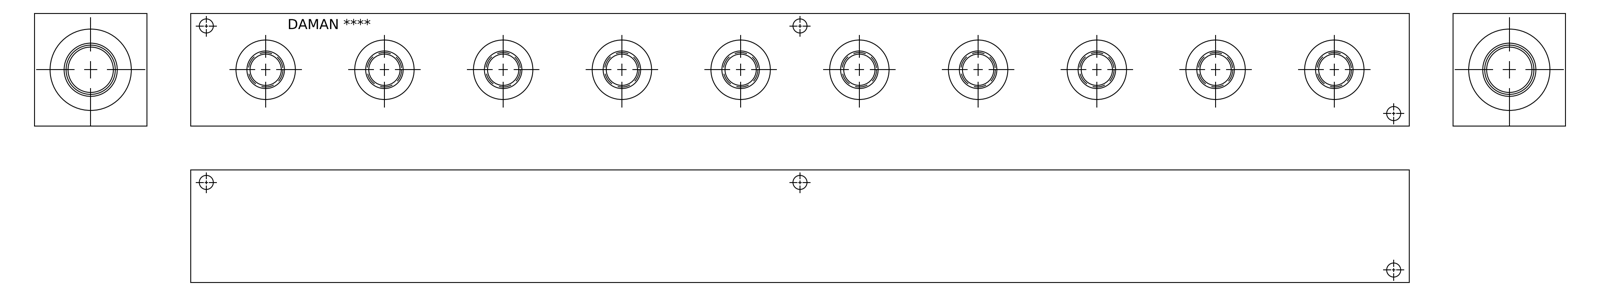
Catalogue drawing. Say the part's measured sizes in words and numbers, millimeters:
The part is named "Part_AH0001008S_3D". Its 3-D file was written by "Autodesk Inventor 2019 (AUTOMOTIVE_DESIGN)". It is 1 solid with 448 faces: 228 planar, 70 cylindrical and 150 other. Overall it measures 619.12 by 57.15 by 57.15 millimeters. Its volume is 1 907 000 cubic millimeters and its surface area 172 896 square millimeters. Round holes: 10 of diameter 17.5, 10 of diameter 19.05, 10 of diameter 19.25, 10 of diameter 30.63, 8 of diameter 15.88, 6 of diameter 7.14, 1 of diameter 23.01, 1 of diameter 24.92, 1 of diameter 26.99, 1 of diameter 27.43, 1 of diameter 42.04. The main face-to-face distances are 57.15, 0.79, 56.36, 619.12, 618.34, 0.78, 617.55, 618.33, 42.09, 14.27. The hole center spacings are 120.65, 60.32, 60.33, 180.98, 301.63, 180.97, 241.3, 361.95.
